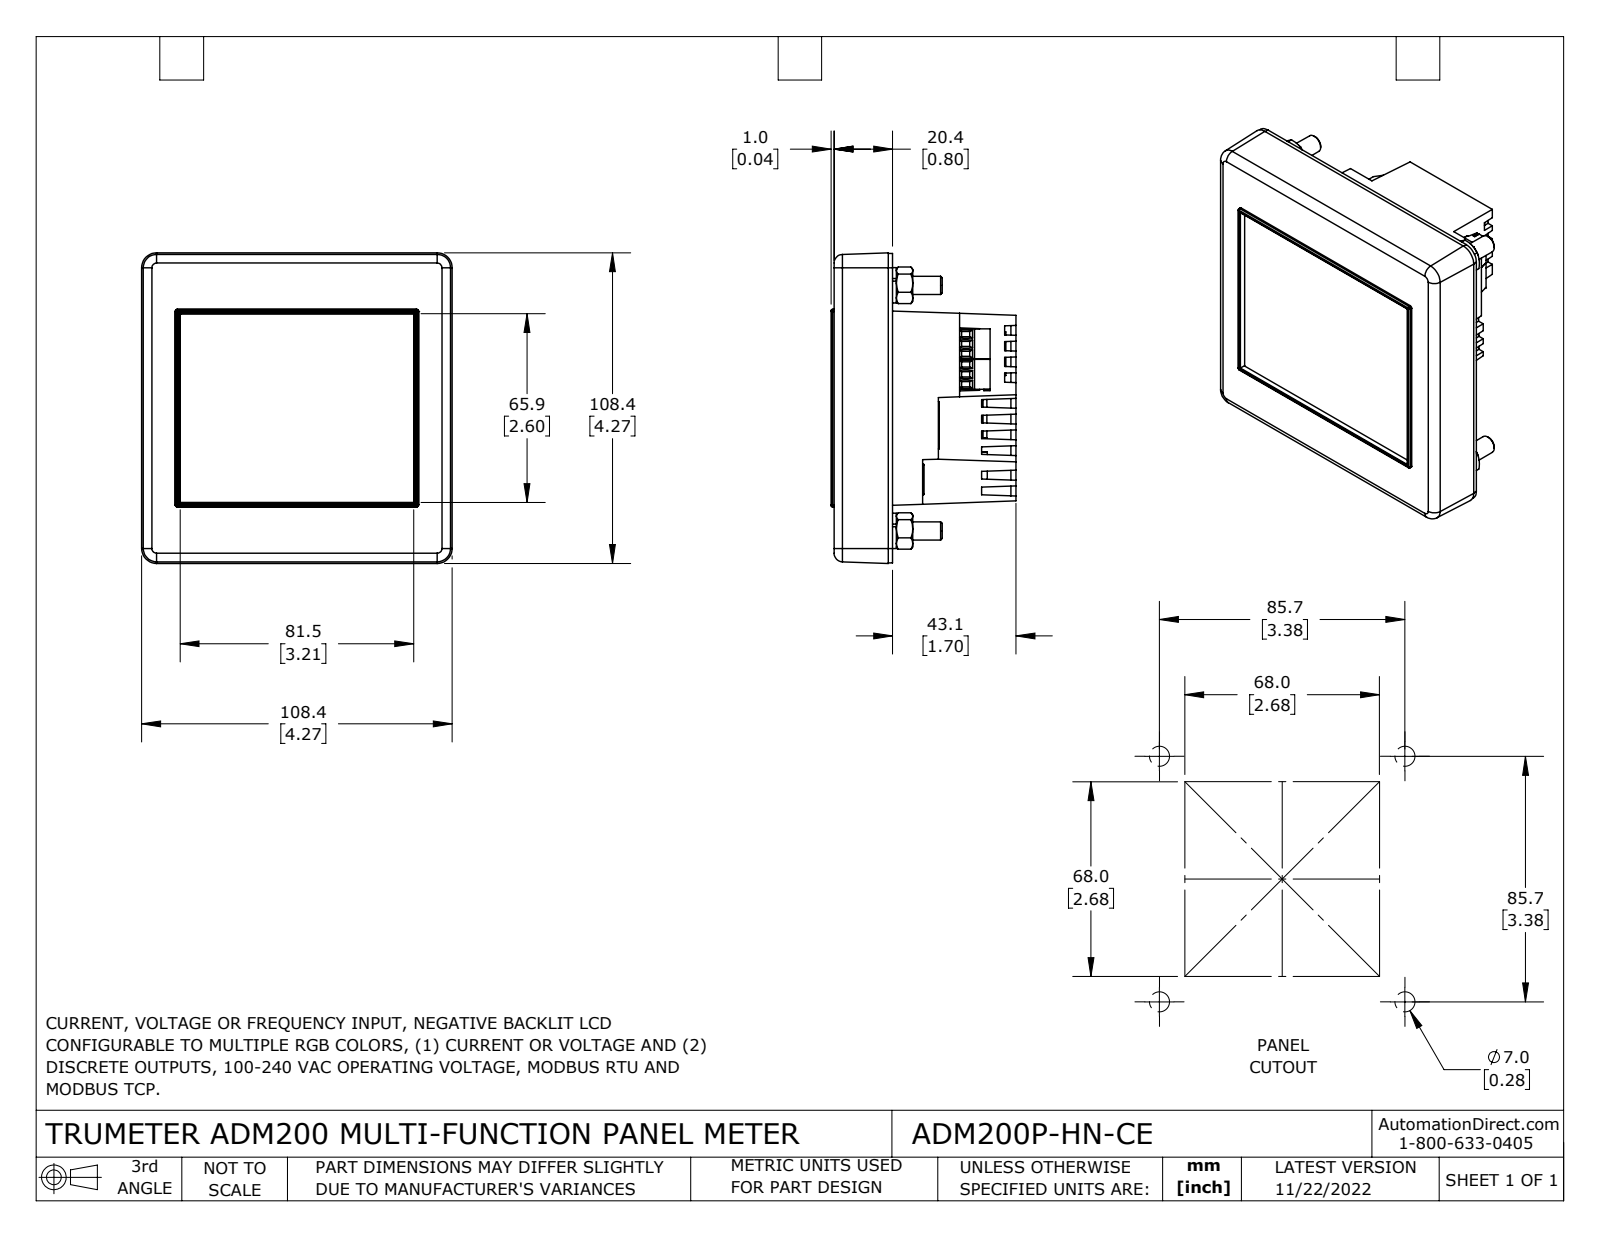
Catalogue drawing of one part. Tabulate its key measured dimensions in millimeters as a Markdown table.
| quantity | value |
| --- | --- |
| part name | ADM200P-HN-CE |
| STEP written by | SolidWorks 2021 (CONFIG_CONTROL_DESIGN) |
| units | millimeters |
| bodies | 23 solids, 2059 faces (1384 planar, 290 cylindrical, 385 other) |
| overall size | 108.4 × 108.4 × 64.5 |
| volume | 128 000 mm³ |
| surface area | 123 100 mm² |
| round holes (diameter × count) | 1.8 × 9, 2.9 × 6, 3 × 5, 5.4 × 4, 6.4 × 4, 6.6 × 4, 7.5 × 4, 3.9 × 2 |
| round bosses / shafts (diameter × count) | 1 × 5, 12.4 × 4, 11.1 × 4, 0.6 × 4, 2 × 2 |
| partial cylindrical surfaces (radius × count) | 0.2 × 32, 0.5 × 30, 1 × 7, 0.4 × 4, 0.8 × 4, 3 × 4, 5 × 4, 0.1 × 2 |
| main face-to-face distances | 0.8, 16.1, 2.8, 1.9, 1.5, 2, 17.6, 86.2, 88.1, 1.2 |
| hole center spacings | 18, 82, 3.5, 7.4, 25, 36, 54, 60.9 |
